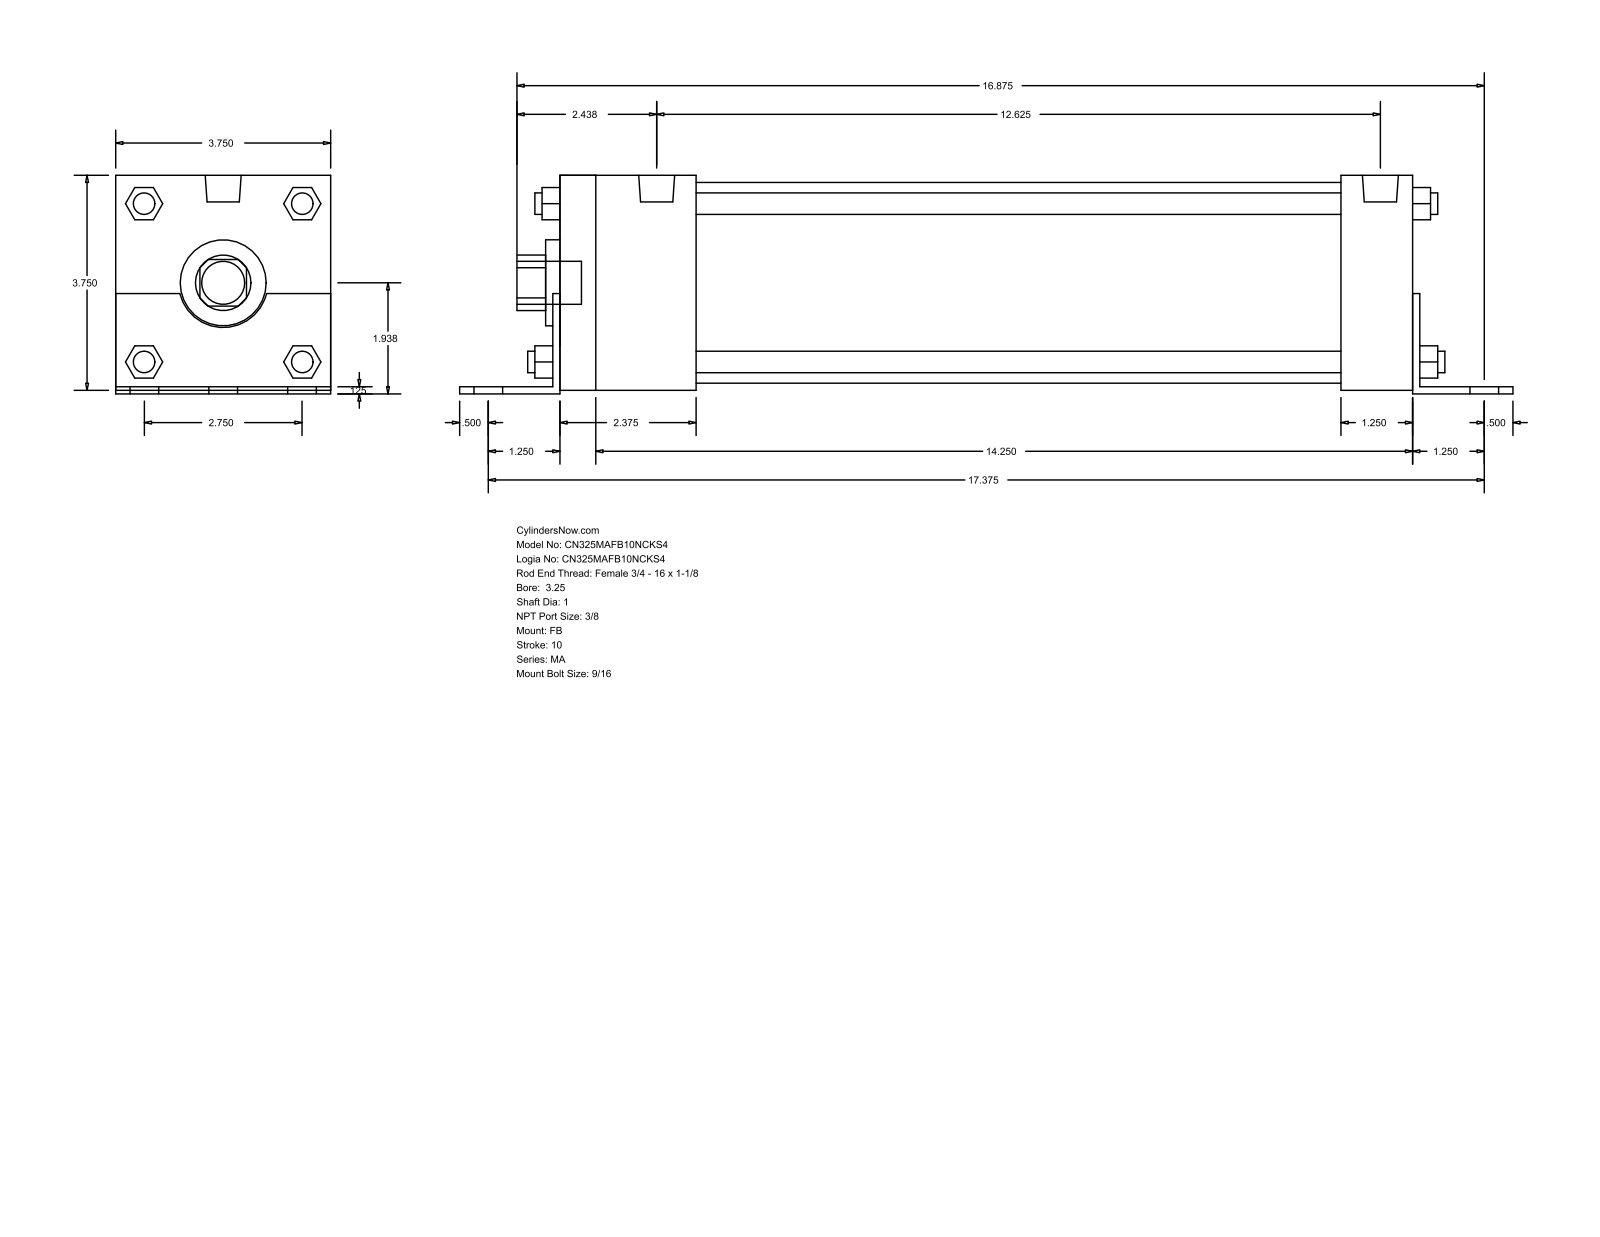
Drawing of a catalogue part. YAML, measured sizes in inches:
part_name: "MA_FB__0325_1"
step_written_by: "GSSL Pune (CONFIG_CONTROL_DESIGN)"
units: inches
bodies: {solids: 0, faces: 140, planar: 105, cylindrical: 35, other: 0}
overall_size: [18.375, 3.813, 3.75]
round_holes:
  - {diameter: 1, count: 1}
  - {diameter: 1.5, count: 1}
  - {diameter: 3.5, count: 1}
round_bosses_or_shafts:
  - {diameter: 0.563, count: 6}
  - {diameter: 0.437, count: 4}
  - {diameter: 0.375, count: 4}
  - {diameter: 0.627, count: 2}
  - {diameter: 0.75, count: 1}
partial_cylinders:
  - {radius: 0.484, count: 1}
  - {radius: 0.78, count: 1}
face_to_face_distances: [3.75, 0.125, 0.063, 3.812, 0.062, 3.687, 15, 14.875, 15.125, 1.375]
